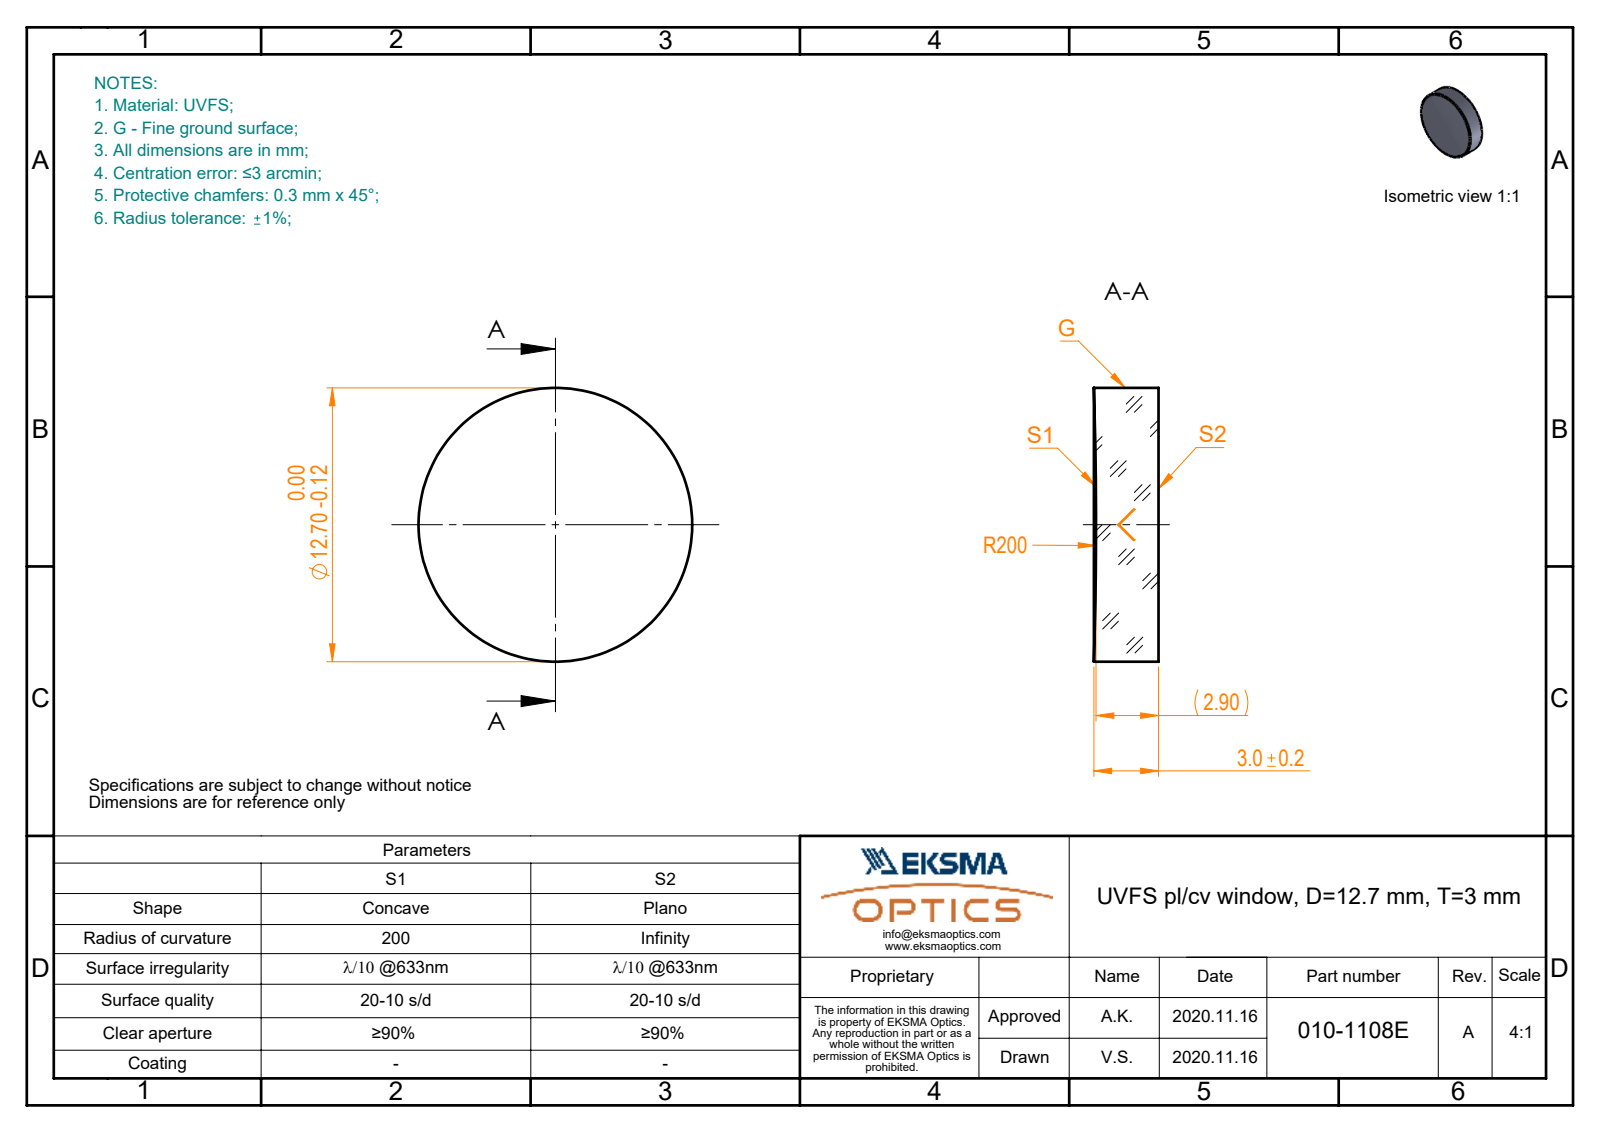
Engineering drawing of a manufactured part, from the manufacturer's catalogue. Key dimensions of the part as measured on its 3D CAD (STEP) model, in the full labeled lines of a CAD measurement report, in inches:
Part name (STEP PRODUCT): 010-1108E_UVFS_PCV_window
STEP written by: SolidWorks 2019 (CONFIG_CONTROL_DESIGN)
Units: inches
Bodies: 1 solid, 5 faces (1 planar, 2 cylindrical, 2 other)
Overall size (bounding box): 0.5 × 0.5 × 0.118
Volume: 0.023 in³ · Surface area: 0.578 in²
Round bosses / shafts (diameter × count): ⌀0.5 ×1
